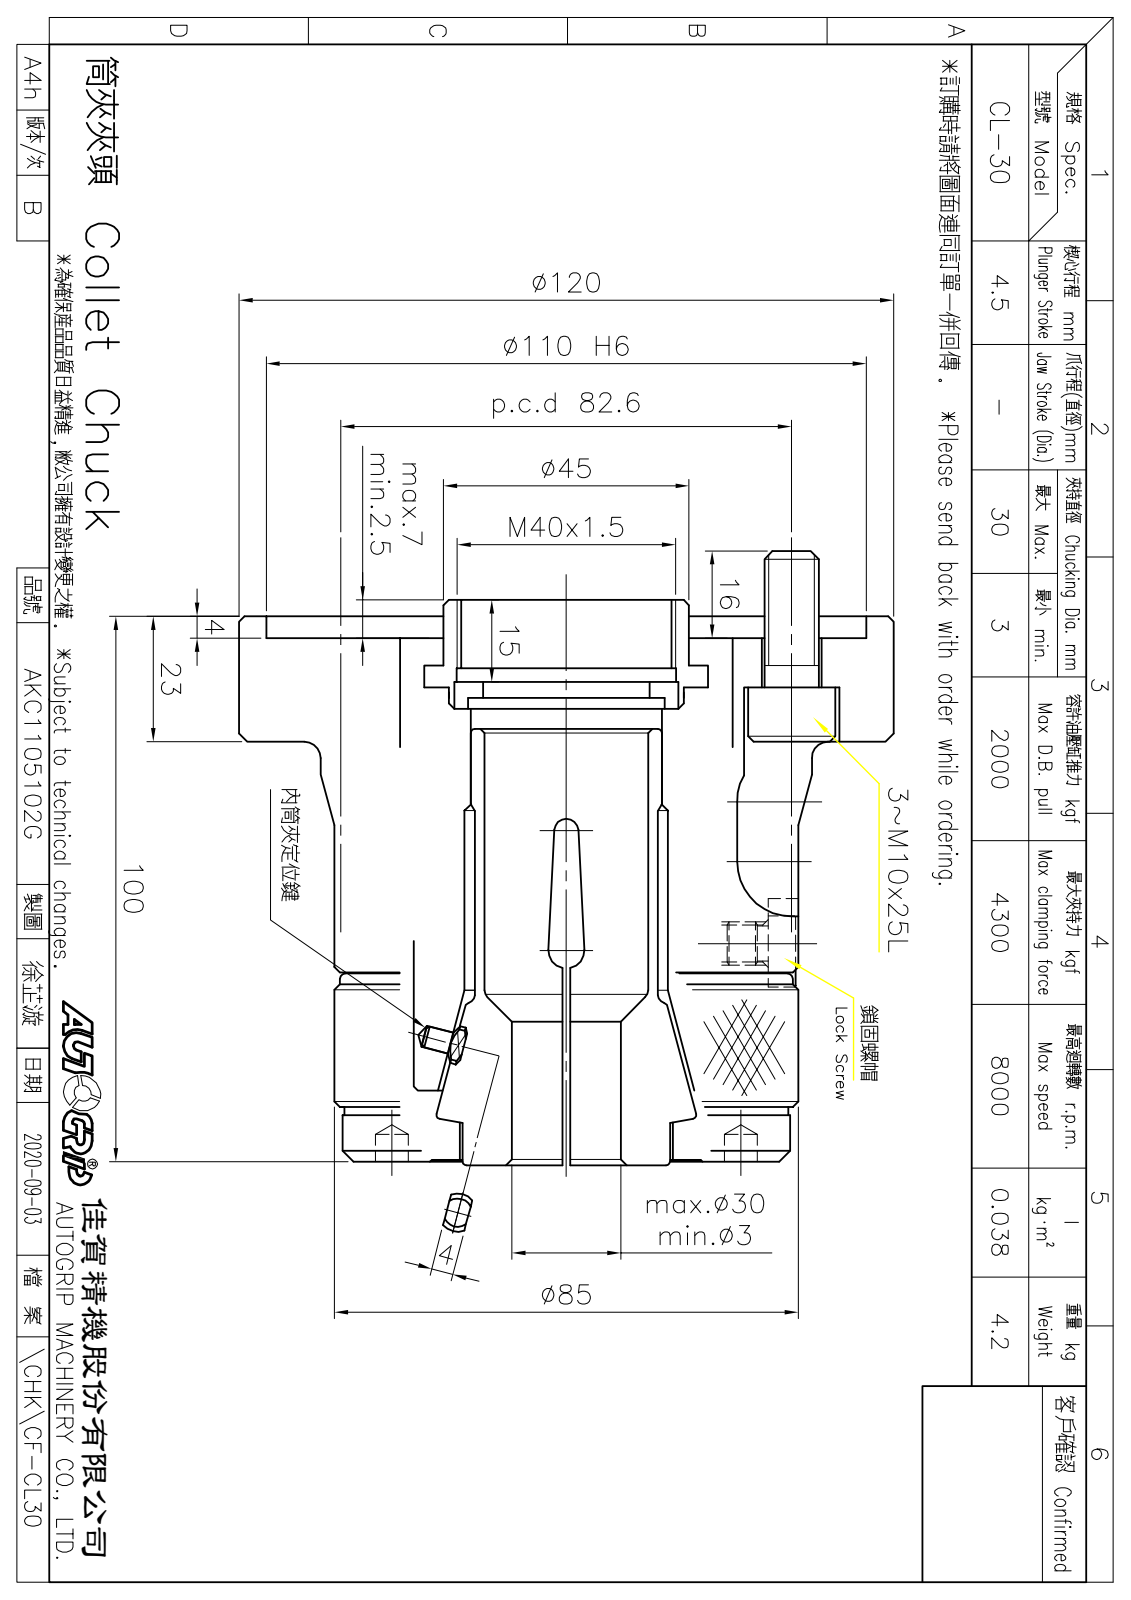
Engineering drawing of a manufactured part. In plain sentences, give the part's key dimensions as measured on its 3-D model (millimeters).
The part is named "CF-CL-30-02000; CF-CL-42-11000; CF-CL-30-01010; CF-CL-30-05000 (+4 more)". Its 3-D file was written by "SolidWorks 2020 (CONFIG_CONTROL_DESIGN)". It is 9 solids with 213 faces: 95 planar, 59 cylindrical and 59 other. Overall it measures 120 by 120 by 112 millimeters. Its volume is 527 274 cubic millimeters and its surface area 130 710 square millimeters. Round holes: 3 of diameter 11, 3 of diameter 17.5, 2 of diameter 5, 1 of diameter 4, 1 of diameter 6.8, 1 of diameter 30.5, 1 of diameter 35, 1 of diameter 36, 1 of diameter 37.3, 1 of diameter 38.5, 1 of diameter 39, 1 of diameter 40.2. Round bosses or shafts: 3 of diameter 16, 3 of diameter 10, 1 of diameter 120, 1 of diameter 90, 1 of diameter 85, 1 of diameter 83, 1 of diameter 82, 1 of diameter 81.4. Partial cylindrical surfaces (rounded edges, fillets, slot ends): 3 of radius 8.5, 3 of radius 10, 1 of radius 3.5, 1 of radius 8, 1 of radius 8.25. The main face-to-face distances are 19, 9, 77, 87, 13, 96, 10, 4, 61.3, 52.3. The hole center spacings are 41.3, 71.54, 21.09, 31.5, 51.94, 70.37, 63.
